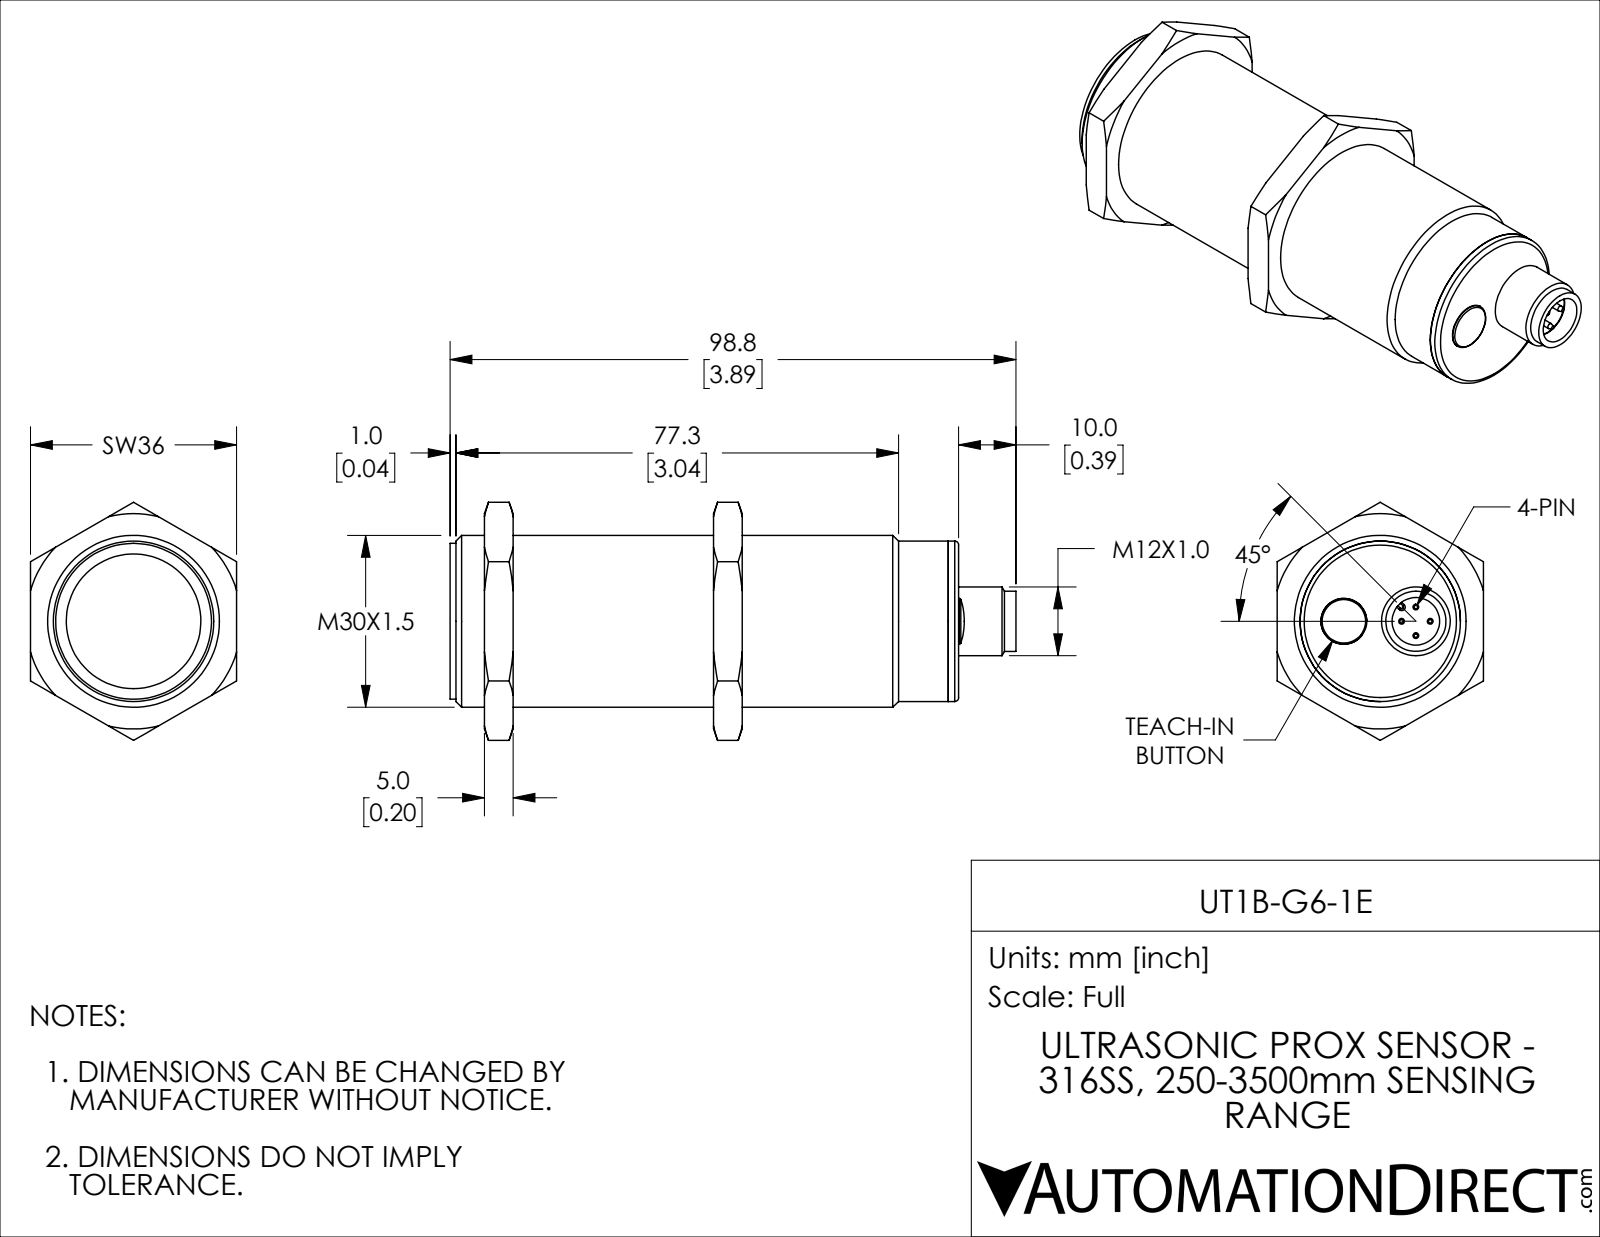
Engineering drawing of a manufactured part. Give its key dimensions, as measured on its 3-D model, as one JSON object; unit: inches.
{"part_name": "UT1B-G6-1E", "step_written_by": "SolidWorks 2018 (AUTOMOTIVE_DESIGN)", "units": "inches", "bodies": {"solids": 7, "faces": 152, "planar": 46, "cylindrical": 49, "other": 57}, "overall_size": [3.89, 1.637, 1.417], "volume_in3": 4.048, "surface_area_in2": 26.65, "round_holes": [[0.071, 4], [0.315, 1], [0.327, 1], [0.372, 1], [0.925, 1], [1.181, 1]], "round_bosses_or_shafts": [[0.039, 4], [1.102, 1], [1.071, 1], [0.472, 1], [0.413, 1], [0.364, 1]], "partial_cylinders_radius": [[0.012, 2], [0.024, 1]], "face_to_face_distances": [3.386, 0.197, 1.417, 1.772, 1.575, 3.457, 0.039, 3.425, 0.394, 0.071], "hole_center_spacings": [0.098, 0.139, 0.197, 0.264, 0.505, 0.146, 0.245, 0.25]}
